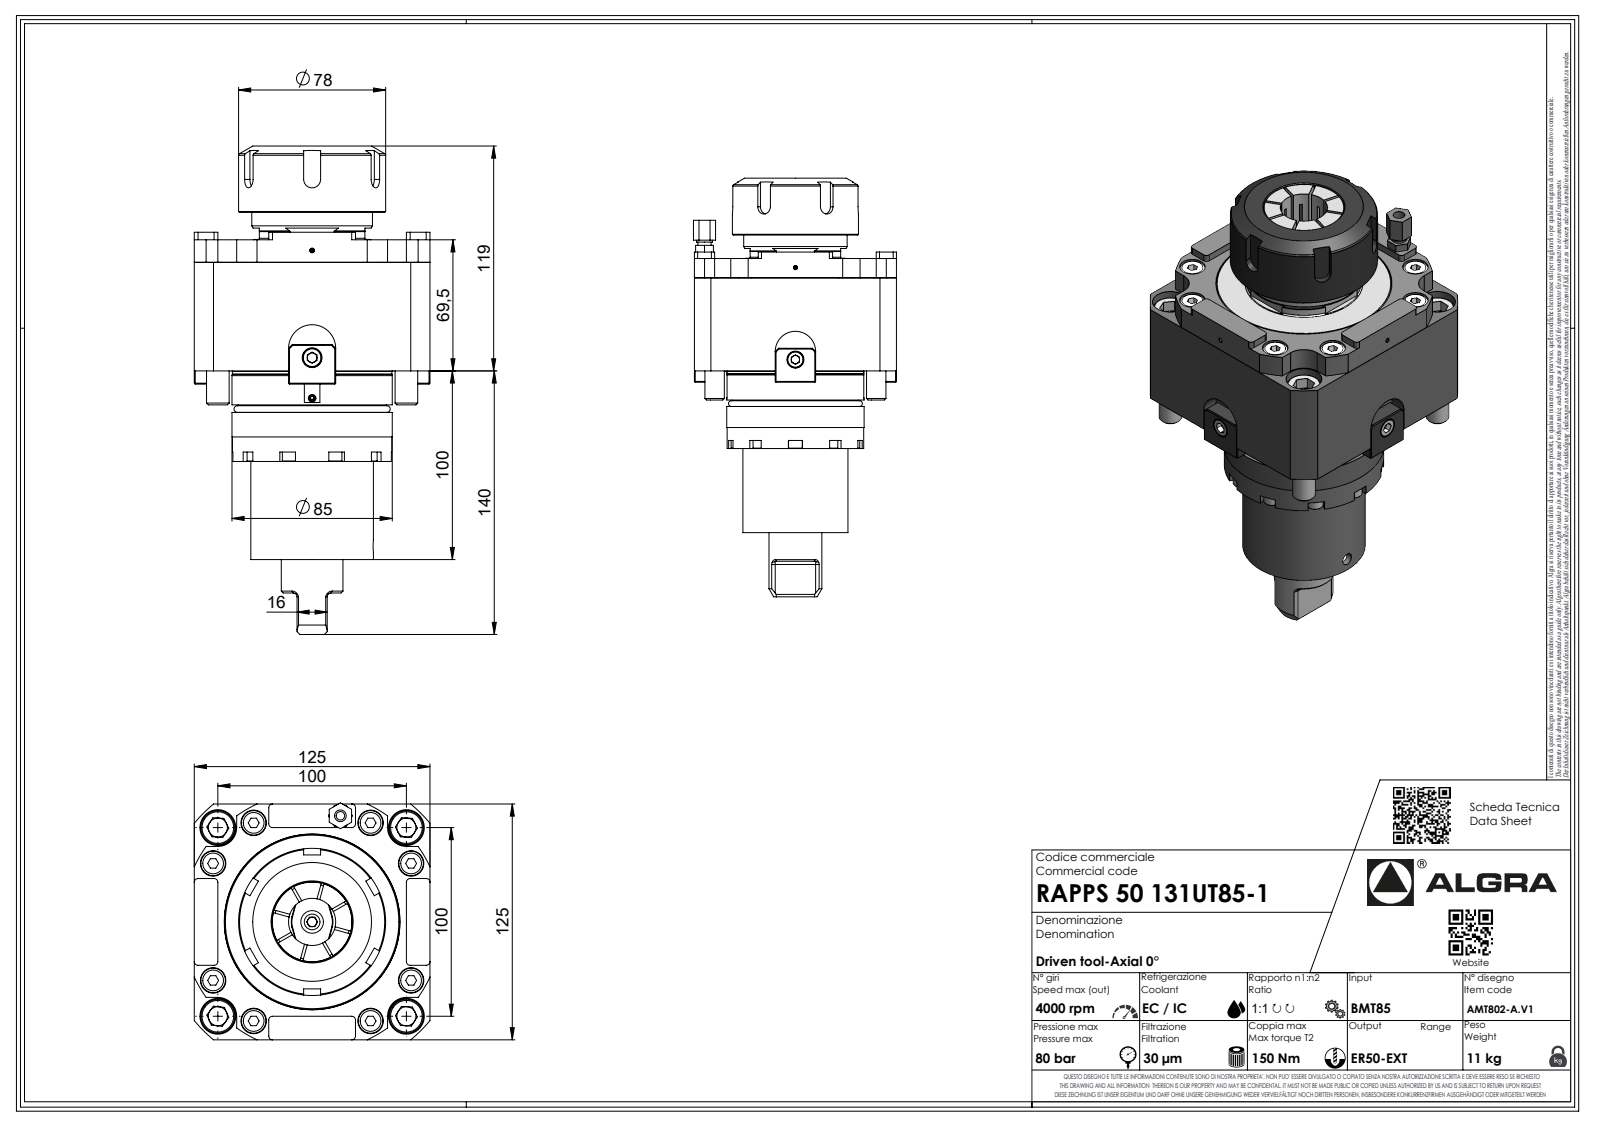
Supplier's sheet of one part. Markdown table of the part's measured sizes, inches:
| quantity | value |
| --- | --- |
| part name | RAPPS50131UT85-1 |
| STEP written by | SolidWorks 2023 (AUTOMOTIVE_DESIGN) |
| units | inches |
| bodies | 1 solid, 654 faces (420 planar, 100 cylindrical, 134 other) |
| overall size | 10.193 × 4.921 × 4.921 |
| volume | 105.4 in³ |
| surface area | 177.6 in² |
| round holes (diameter × count) | 0.177 × 2, 0.083 × 1 |
| round bosses / shafts (diameter × count) | 0.472 × 3, 3.346 × 1, 3.331 × 1, 3.327 × 1, 3.071 × 1, 2.559 × 1, 2.52 × 1, 1.287 × 1 |
| partial cylindrical surfaces (radius × count) | 0.079 × 22, 0.171 × 10, 0.013 × 7, 0.02 × 7, 0.146 × 7, 0.394 × 4, 0.177 × 3, 0.492 × 2 |
| main face-to-face distances | 4.921, 2.732, 2.736, 4.693, 1.961, 1.957, 3.937, 0.472, 6.669, 6.673 |
